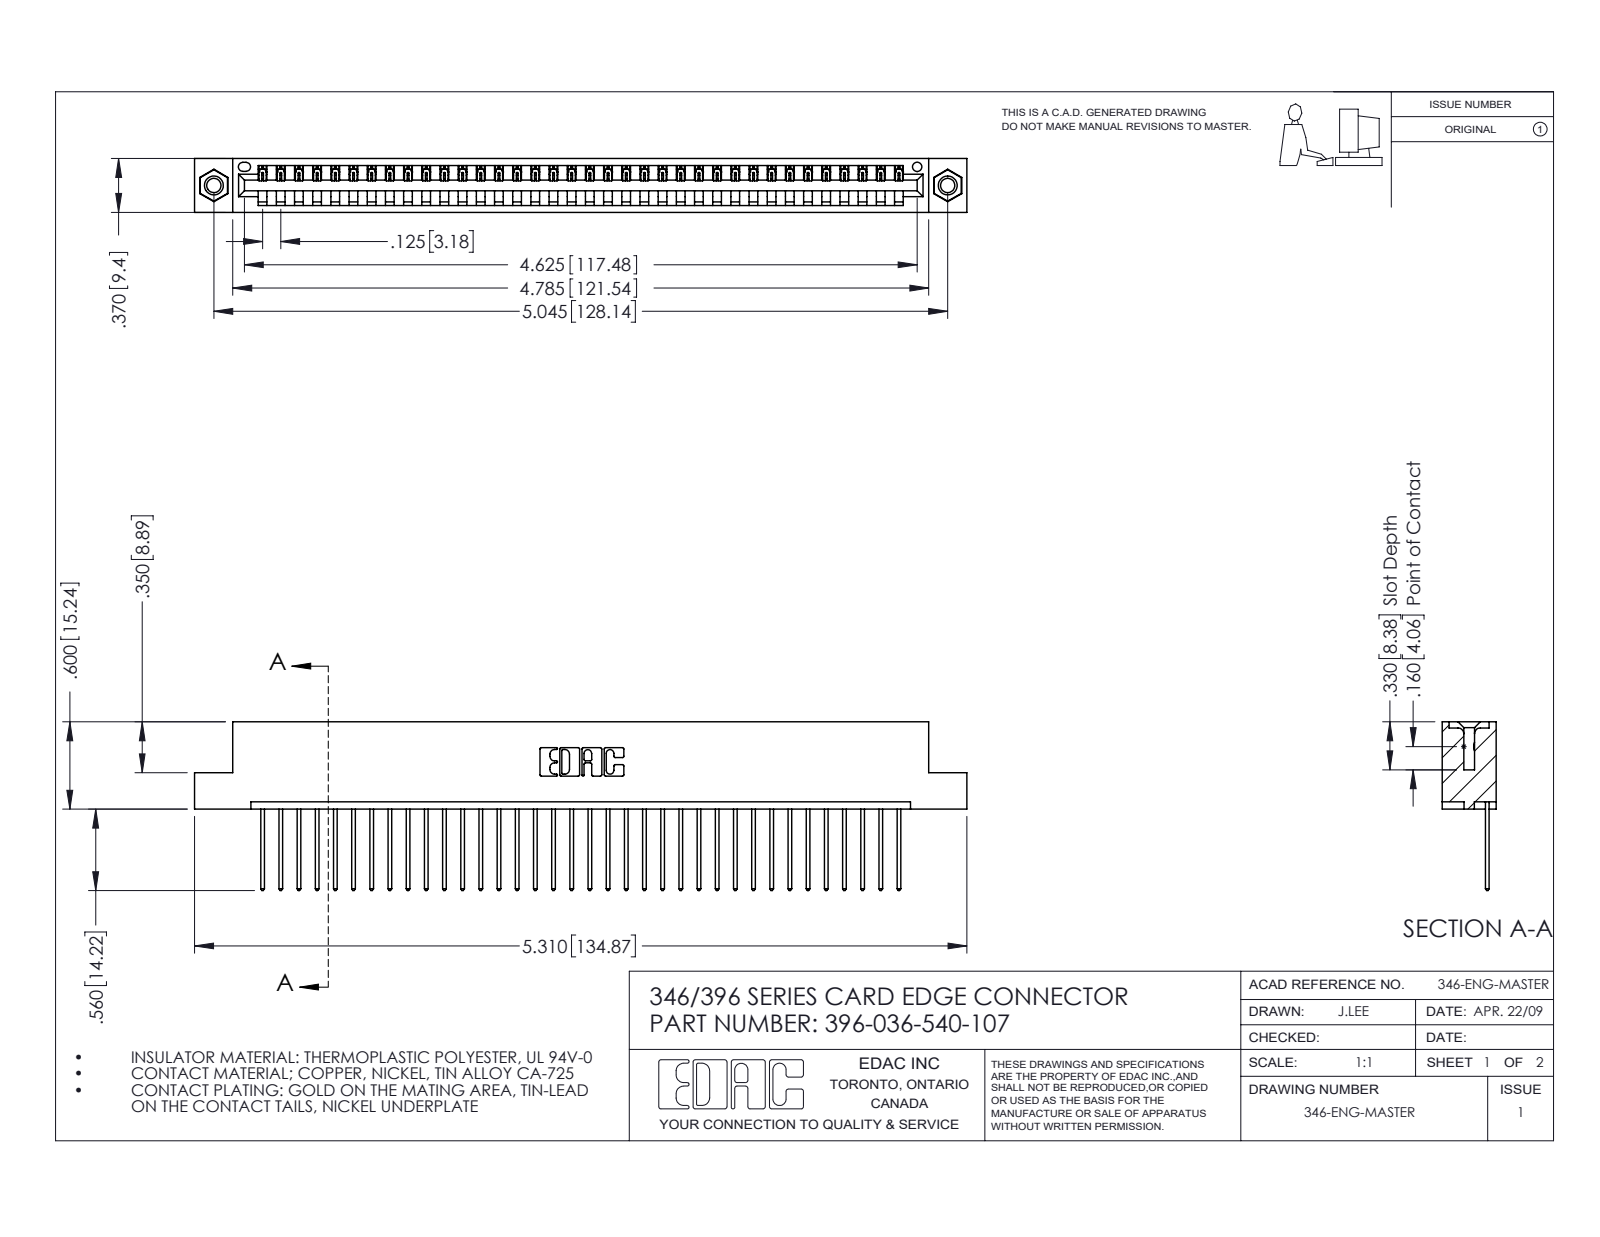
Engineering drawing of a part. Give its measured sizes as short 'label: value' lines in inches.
name: 396-036-540-107; 345-250-001_345-250-005-103; 345-292-001_345-293-140; 346 Part_Flush Mounting Lugs - 0.156 Dia-TI
written by: SolidWorks 2016 (CONFIG_CONTROL_DESIGN)
unit: in
bodies: 39 solids, 2270 faces (1548 planar, 706 cylindrical, 16 other)
size: 5.31 × 1.16 × 0.37
volume: 0.787 in³; area: 25.5 in²
holes: 2× ⌀0.098, 2× ⌀0.125, 2× ⌀0.156, 1× ⌀0.064
bosses: 2× ⌀0.155
rounds: 72× R0.006, 72× R0.01, 22× R0.01, 6× R0.007, 6× R0.031, 3× R0.026, 2× R0.031, 2× R0.04
face distances: 0.048, 0.322, 0.37, 0.25, 0.072, 0.298, 0.025, 0.148, 0.222, 0.1
hole spacings: 0.246, 4.836, 5.045
